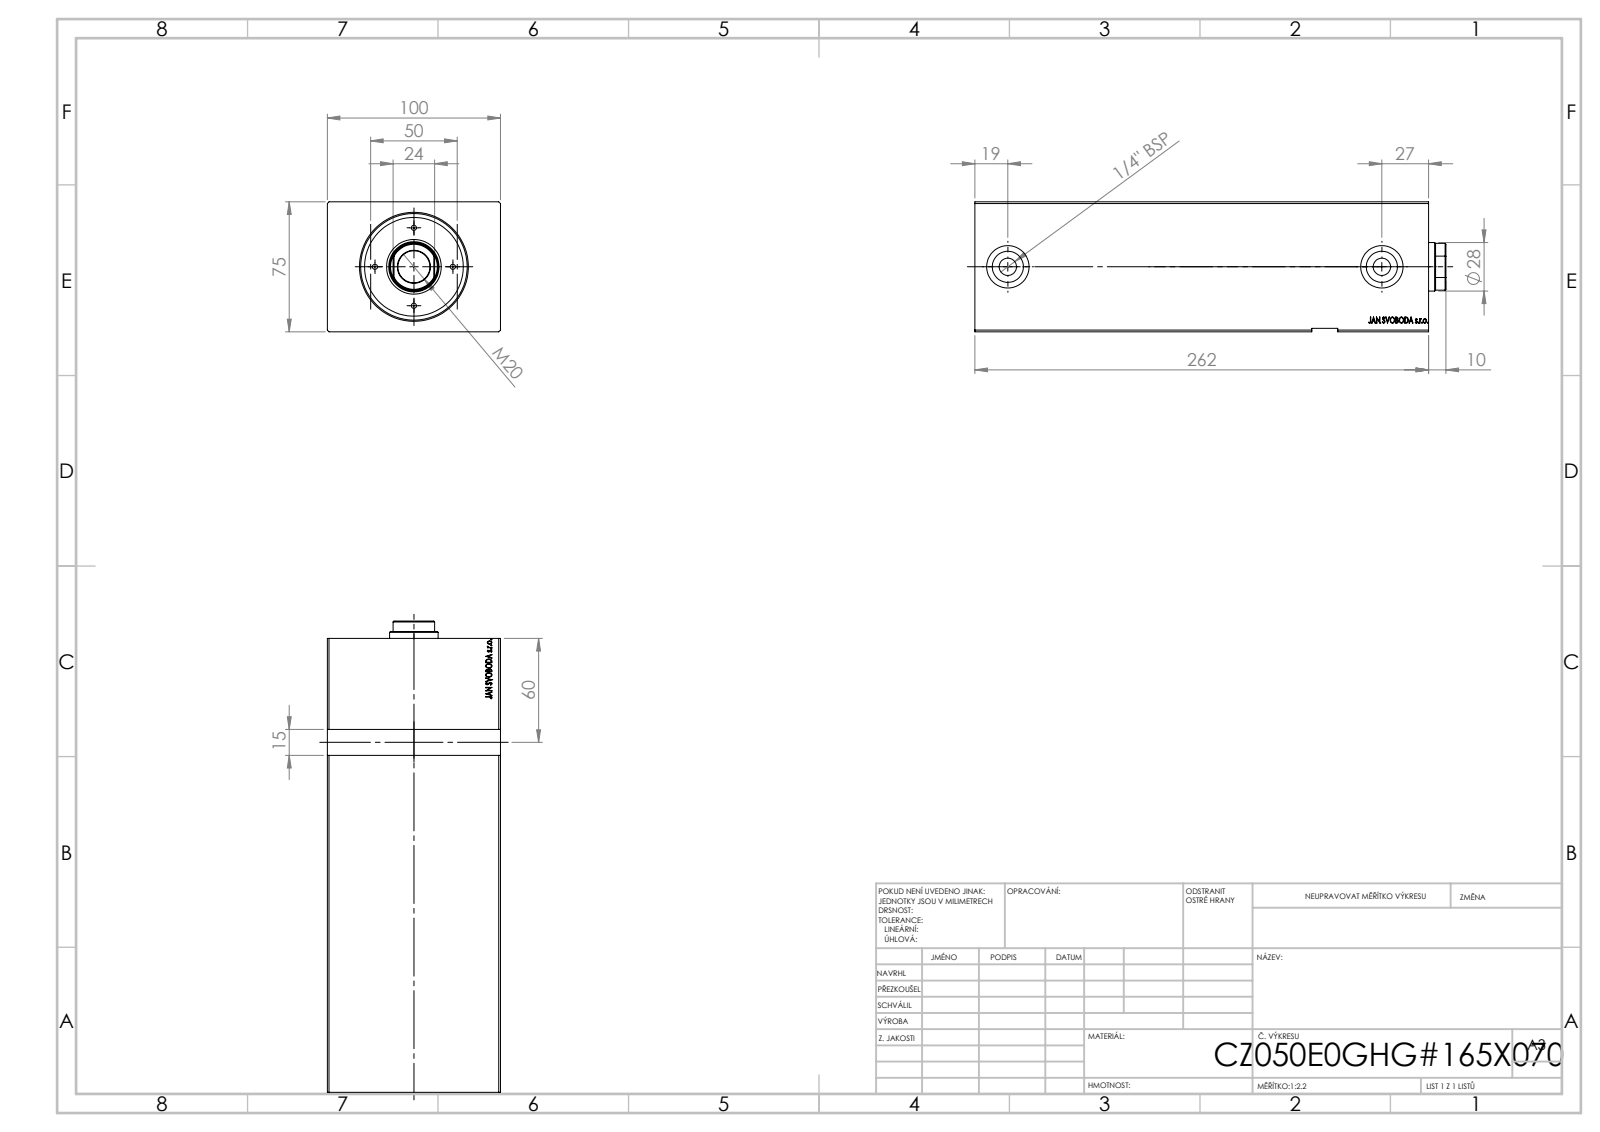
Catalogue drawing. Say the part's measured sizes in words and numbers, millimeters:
Its 3-D file was written by "SolidWorks 2019 (CONFIG_CONTROL_DESIGN)". It is 1 solid with 799 faces: 395 planar, 22 cylindrical and 382 other. Overall it measures 262 by 100 by 75 millimeters. Its volume is 1 463 000 cubic millimeters and its surface area 147 313 square millimeters. Round holes: 2 of diameter 8, 2 of diameter 10, 2 of diameter 18, 2 of diameter 24.5, 1 of diameter 36, 1 of diameter 50, 1 of diameter 61.5. The main face-to-face distances are 75, 100, 262, 244.2, 17.8, 2, 73, 261.8, 17.6, 10. The hole center spacings are 196, 216.
